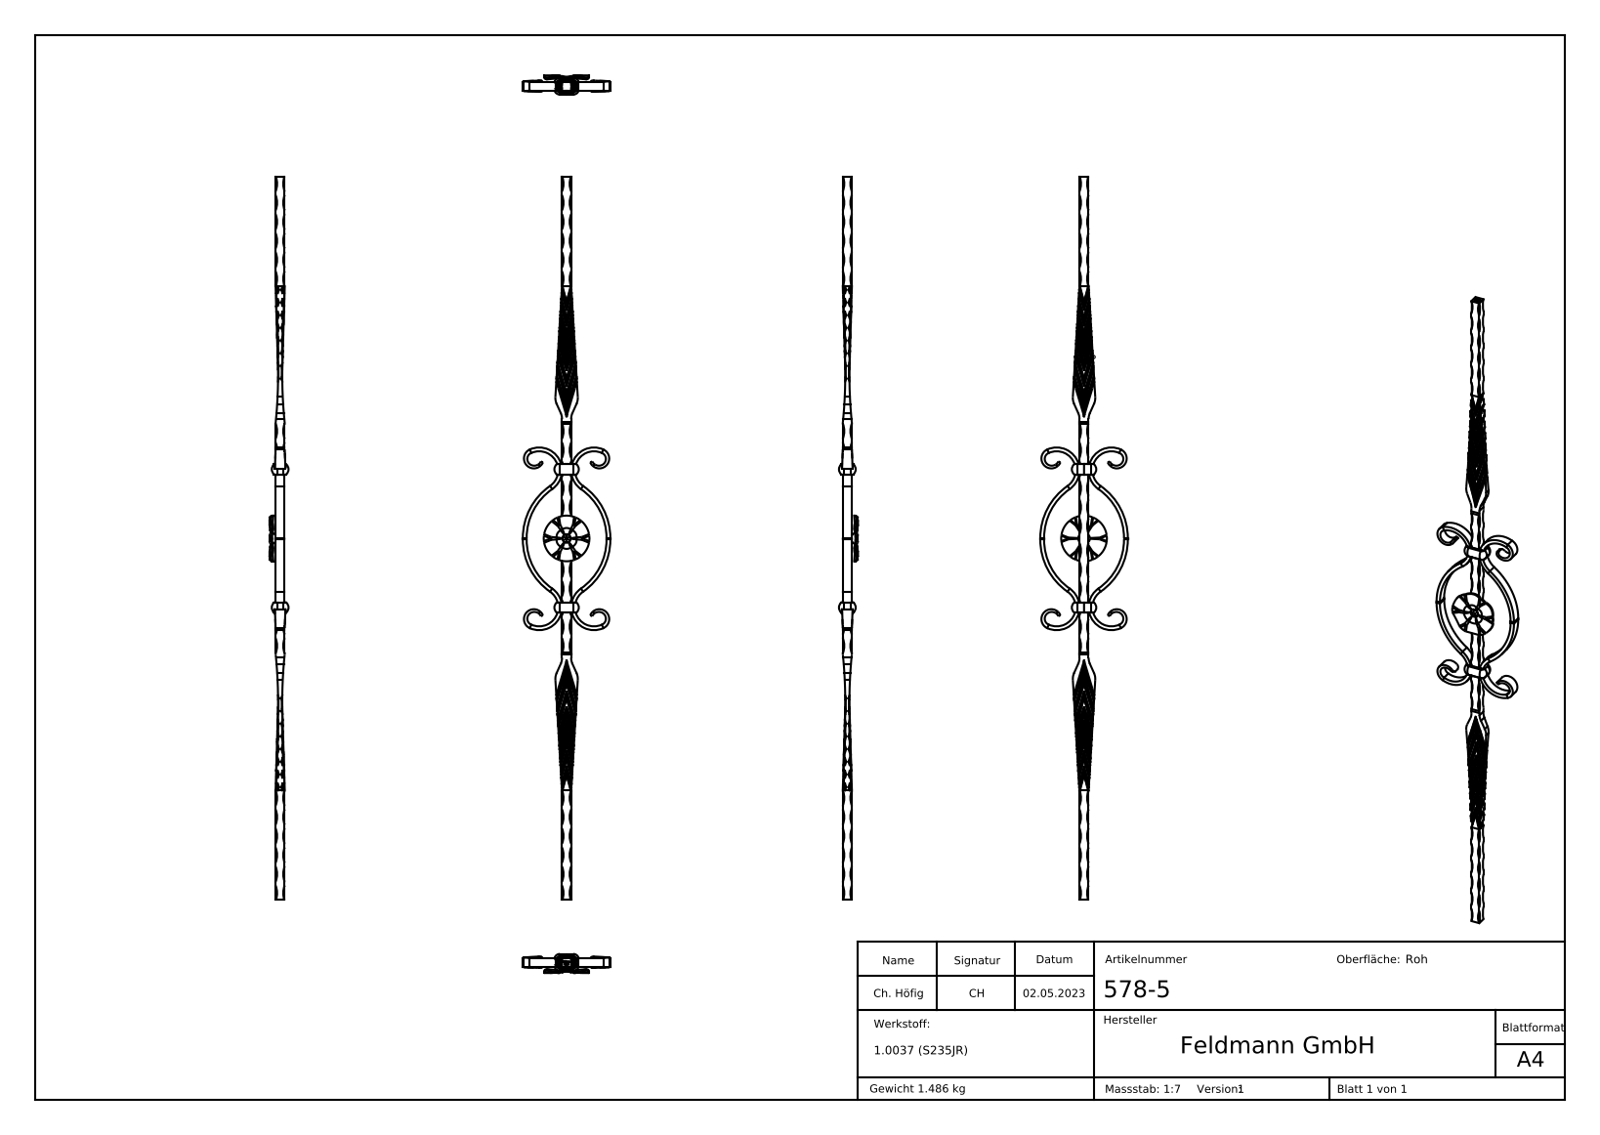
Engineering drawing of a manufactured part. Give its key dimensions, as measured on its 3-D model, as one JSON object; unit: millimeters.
{"part_name": "578-5", "step_written_by": "SolidWorks 2018 (CONFIG_CONTROL_DESIGN)", "units": "millimeters", "bodies": {"solids": 7, "faces": 1228, "planar": 507, "cylindrical": 275, "other": 446}, "overall_size": [950, 115, 25], "volume_mm3": 190473, "surface_area_mm2": 92100, "round_bosses_or_shafts": [[60, 1]], "partial_cylinders_radius": [[1, 88], [0.2, 80], [2, 20], [8.75, 8], [20, 8], [25.02, 4], [30, 4], [30.02, 4]], "face_to_face_distances": [12, 4.06, 2.12, 8.12, 79.44, 1.94, 83.5, 6.18, 75.38, 6]}
